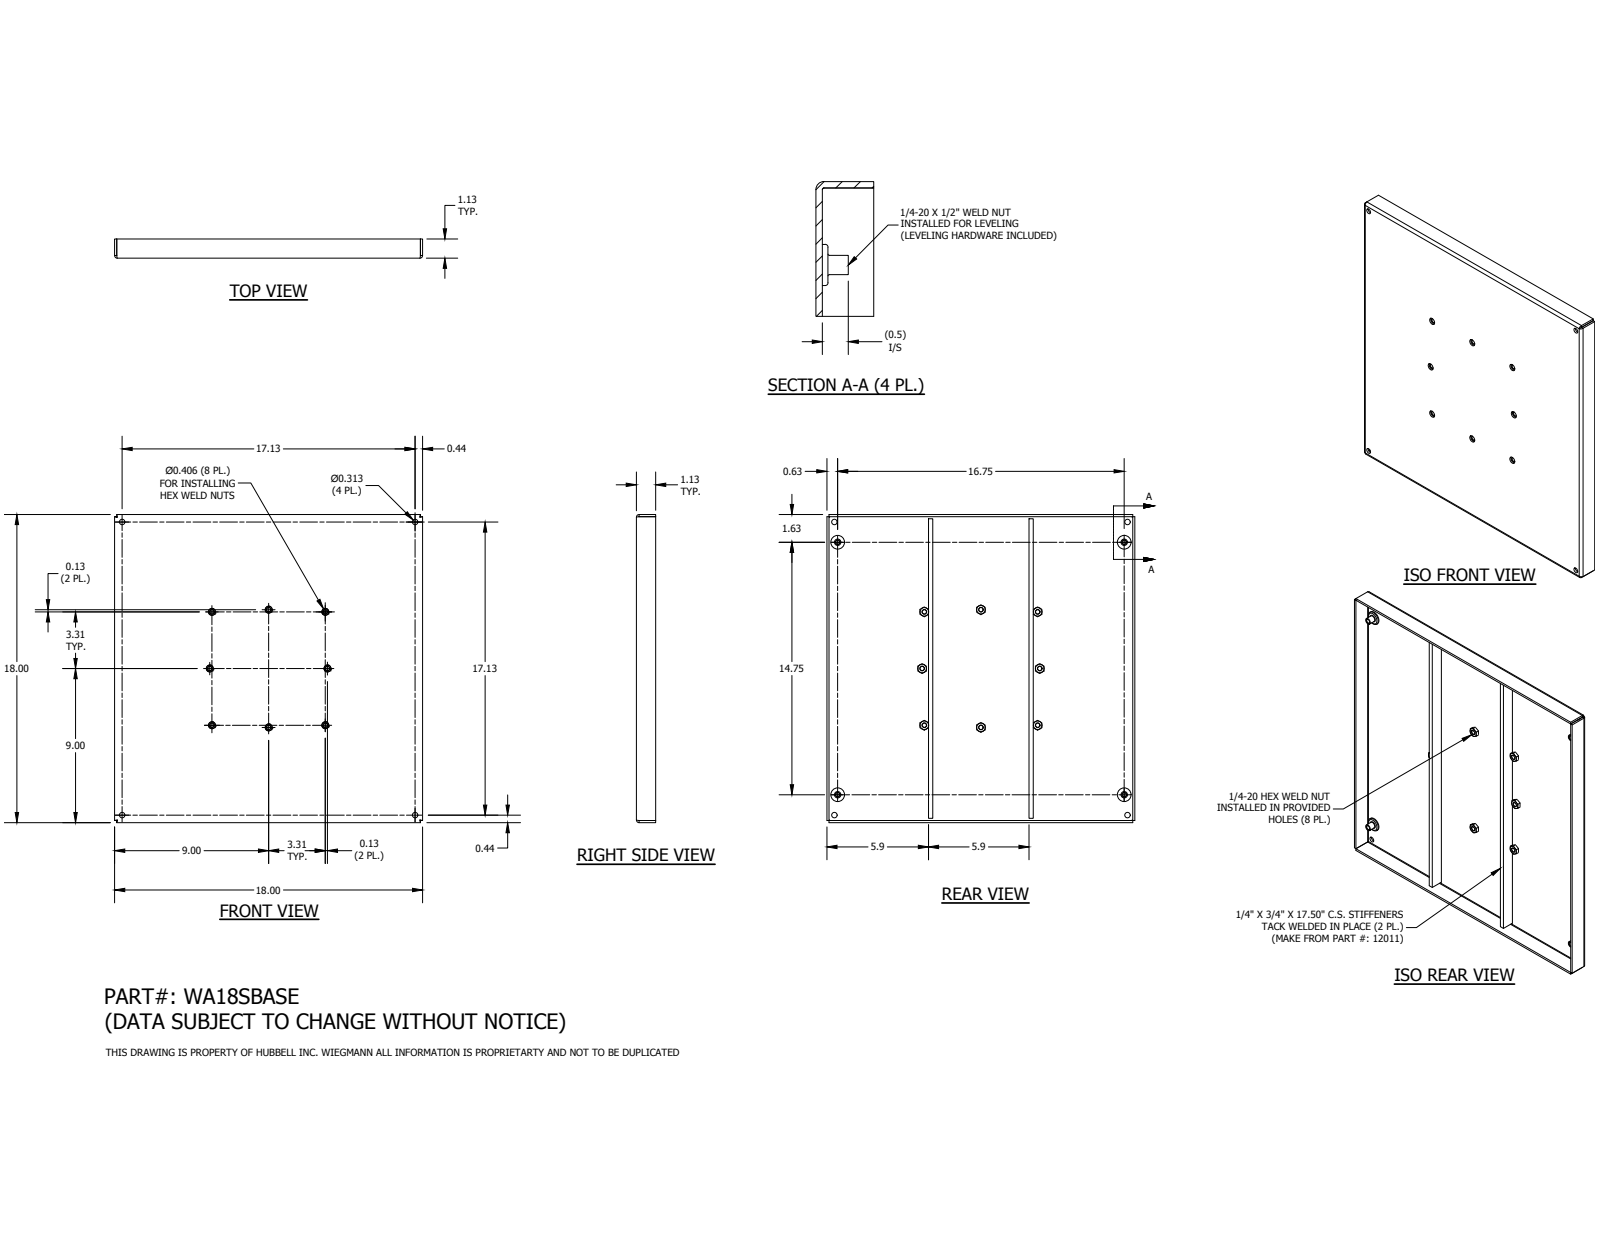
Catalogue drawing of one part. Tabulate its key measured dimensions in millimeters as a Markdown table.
| quantity | value |
| --- | --- |
| part name | WA18SBASEB; 12011_17.5_INCH; 34981; 34958 (+1 more) |
| STEP written by | Autodesk Inventor 2016 (AUTOMOTIVE_DESIGN) |
| units | millimeters |
| bodies | 15 solids, 314 faces (146 planar, 72 cylindrical, 96 other) |
| overall size | 457.2 × 457.2 × 28.57 |
| volume | 917 234 mm³ |
| surface area | 567 046 mm² |
| round holes (diameter × count) | 6.35 × 12, 10.32 × 8, 7.94 × 4 |
| round bosses / shafts (diameter × count) | 10.31 × 8, 20.32 × 4, 9.52 × 4 |
| partial cylindrical surfaces (radius × count) | 1.03 × 21, 0.79 × 4, 3.97 × 4 |
| main face-to-face distances | 3.18, 6.35, 450.85, 3.17, 454.02, 457.2, 454.03, 306.39, 150.81, 157.16 |
| hole center spacings | 84.2, 190.98, 253.47, 329.79, 374.44, 30.54, 123.47, 168.28 |
